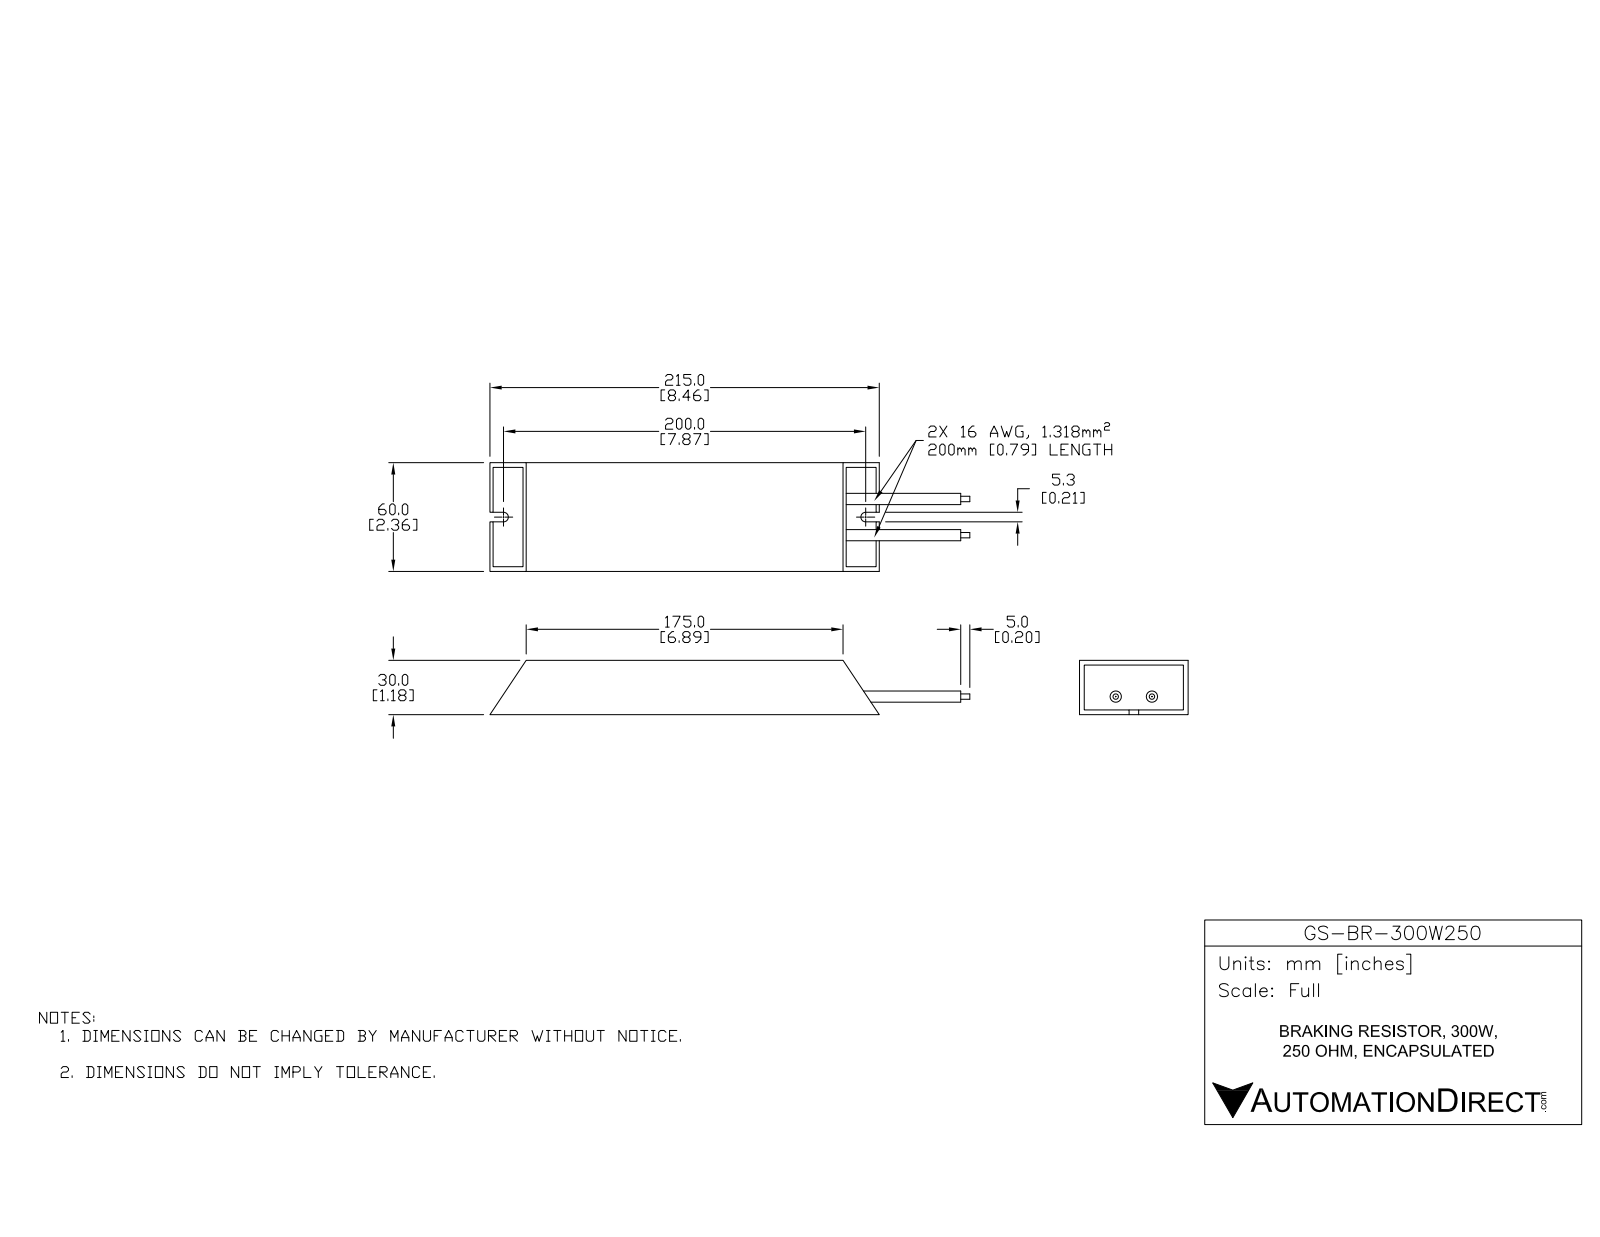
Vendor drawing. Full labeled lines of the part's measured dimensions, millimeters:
Part name (STEP PRODUCT): GS-BR-300W250
STEP written by: SolidWorks 2015 (AUTOMOTIVE_DESIGN)
Units: millimetres
Bodies: 1 solid, 34 faces (24 planar, 10 cylindrical, 0 other)
Overall size (bounding box): 265 × 60 × 30
Volume: 327 600 mm³ · Surface area: 44 580 mm²
Round bosses / shafts (diameter × count): ⌀6.2 ×2, ⌀3 ×2
Partial cylindrical surfaces — rounded edges, fillets, slot ends (radius × count): R2.6 ×2
Main face-to-face distances: 30, 60, 2.6, 27.4, 175, 57.4, 54.8, 24.8, 27.4, 32.6
